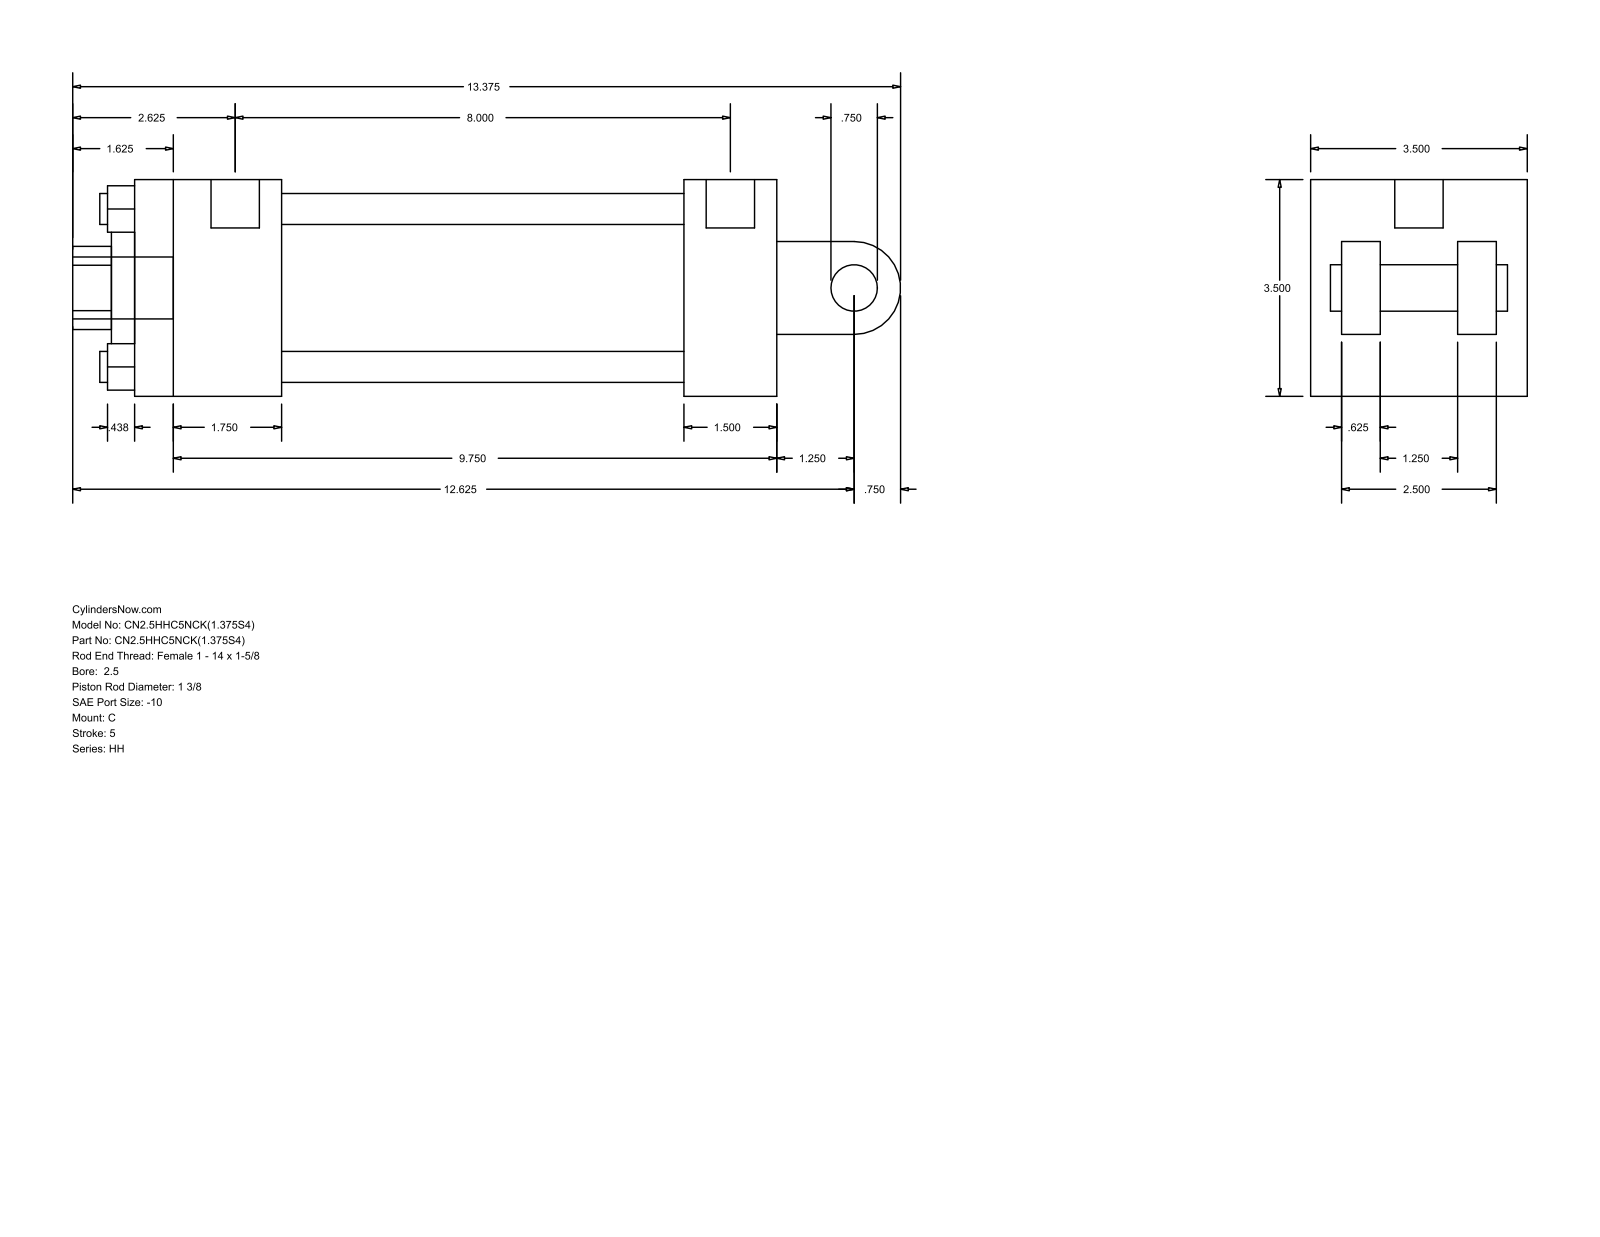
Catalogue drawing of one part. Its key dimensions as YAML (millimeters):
part_name: "HH_C__0250_1.375"
step_written_by: "GSSL Pune (CONFIG_CONTROL_DESIGN)"
units: millimeters
bodies: {solids: 0, faces: 99, planar: 70, cylindrical: 29, other: 0}
overall_size: [339.73, 88.9, 88.9]
round_holes:
  - {diameter: 12.7, count: 4}
  - {diameter: 5.56, count: 2}
  - {diameter: 19.84, count: 1}
  - {diameter: 34.92, count: 1}
  - {diameter: 50.8, count: 1}
  - {diameter: 73.03, count: 1}
round_bosses_or_shafts:
  - {diameter: 5.56, count: 2}
  - {diameter: 25.4, count: 1}
  - {diameter: 19.84, count: 1}
  - {diameter: 19.05, count: 1}
partial_cylinders:
  - {radius: 17.06, count: 1}
  - {radius: 19.05, count: 1}
face_to_face_distances: [88.9, 263.53, 63.5, 15.87, 12.7, 225.42, 38.11, 60.32, 165.1, 203.21]
hole_center_spacings: [45.79, 64.76, 91.58, 1.58]
